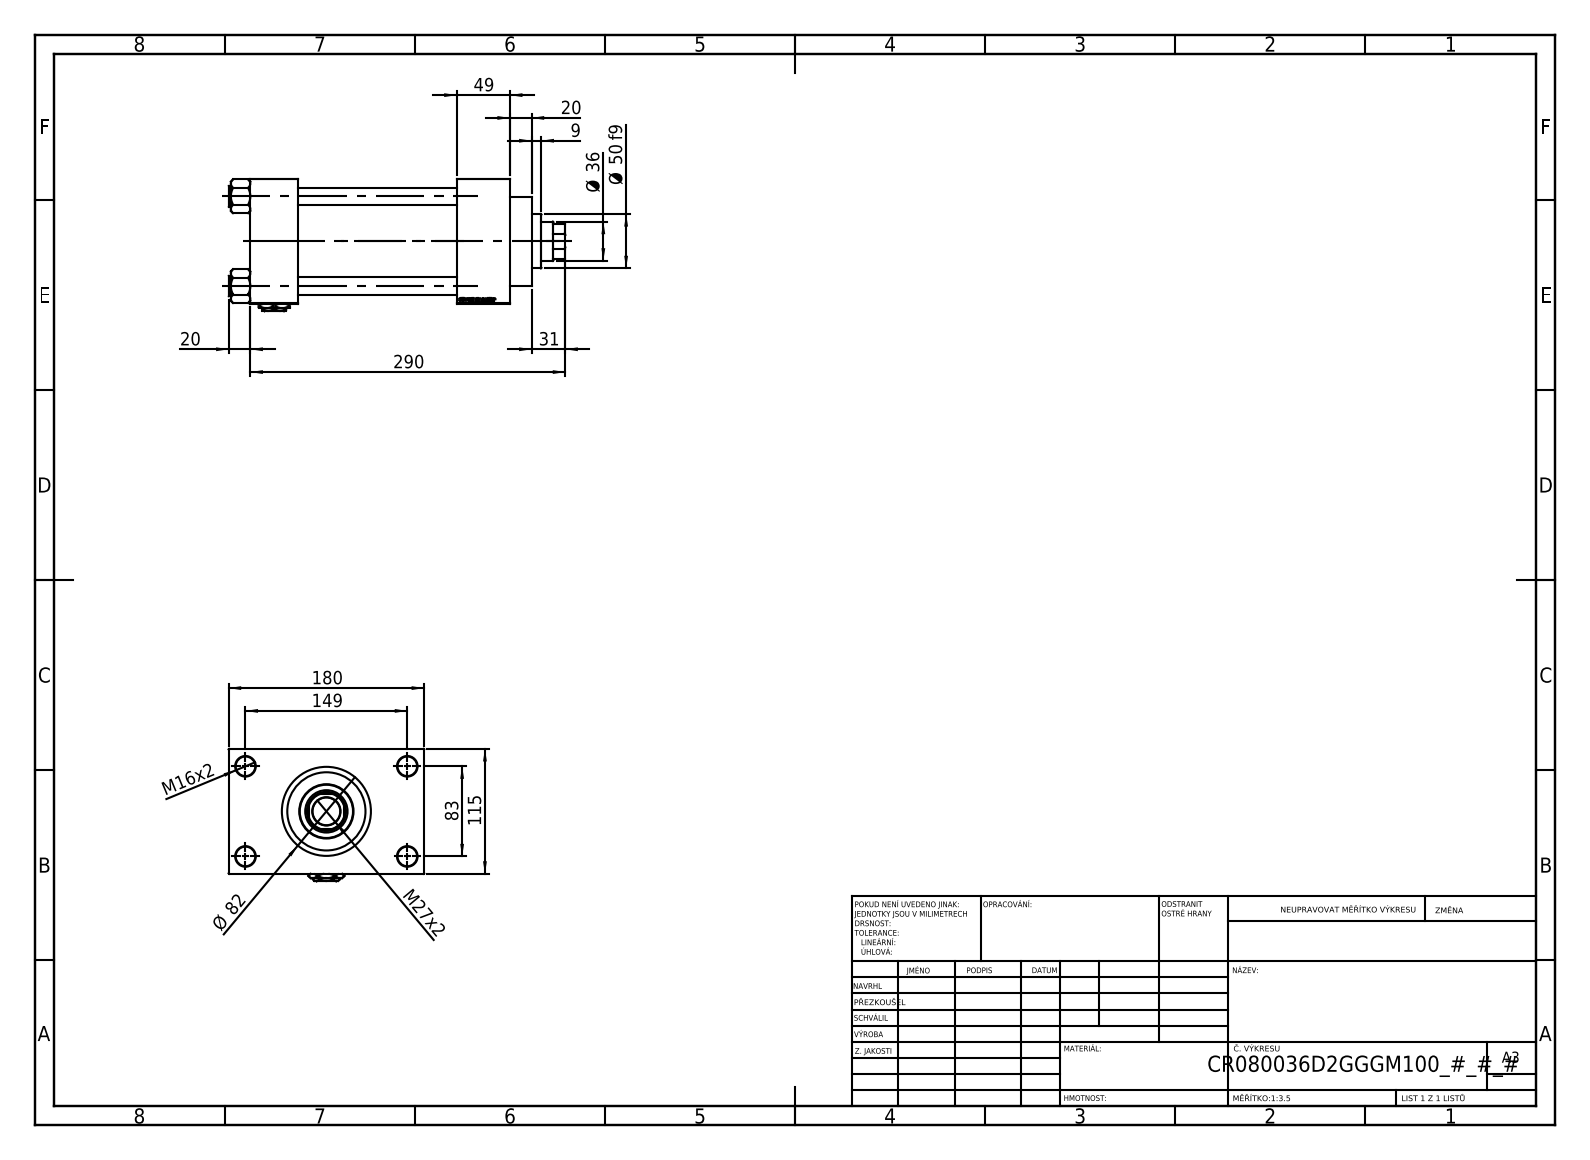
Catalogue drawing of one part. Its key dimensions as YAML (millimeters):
part_name: "V215_VC_A; Zatka_pro_OIL_PORT; V215CR_VCP_D; NUT_M5_D (+2 more)"
step_written_by: "SolidWorks 2019 (CONFIG_CONTROL_DESIGN)"
units: millimeters
bodies: {solids: 12, faces: 1205, planar: 569, cylindrical: 96, other: 540}
overall_size: [310, 180, 122]
volume: 2202000
surface_area: 364543
round_holes:
  - {diameter: 16, count: 4}
  - {diameter: 18, count: 4}
  - {diameter: 7, count: 2}
  - {diameter: 26.44, count: 2}
  - {diameter: 35, count: 2}
  - {diameter: 25.5, count: 1}
  - {diameter: 36, count: 1}
  - {diameter: 39, count: 1}
  - {diameter: 61, count: 1}
  - {diameter: 72, count: 1}
  - {diameter: 80, count: 1}
round_bosses_or_shafts:
  - {diameter: 19, count: 4}
  - {diameter: 86, count: 1}
  - {diameter: 82, count: 1}
  - {diameter: 50, count: 1}
partial_cylinders:
  - {radius: 17.5, count: 1}
face_to_face_distances: [115, 146, 195, 49, 44, 190, 239, 32.5, 147.5, 180]
hole_center_spacings: [33.15, 58.48, 82.7, 85.28, 89.24, 115.85, 142.43, 83]
